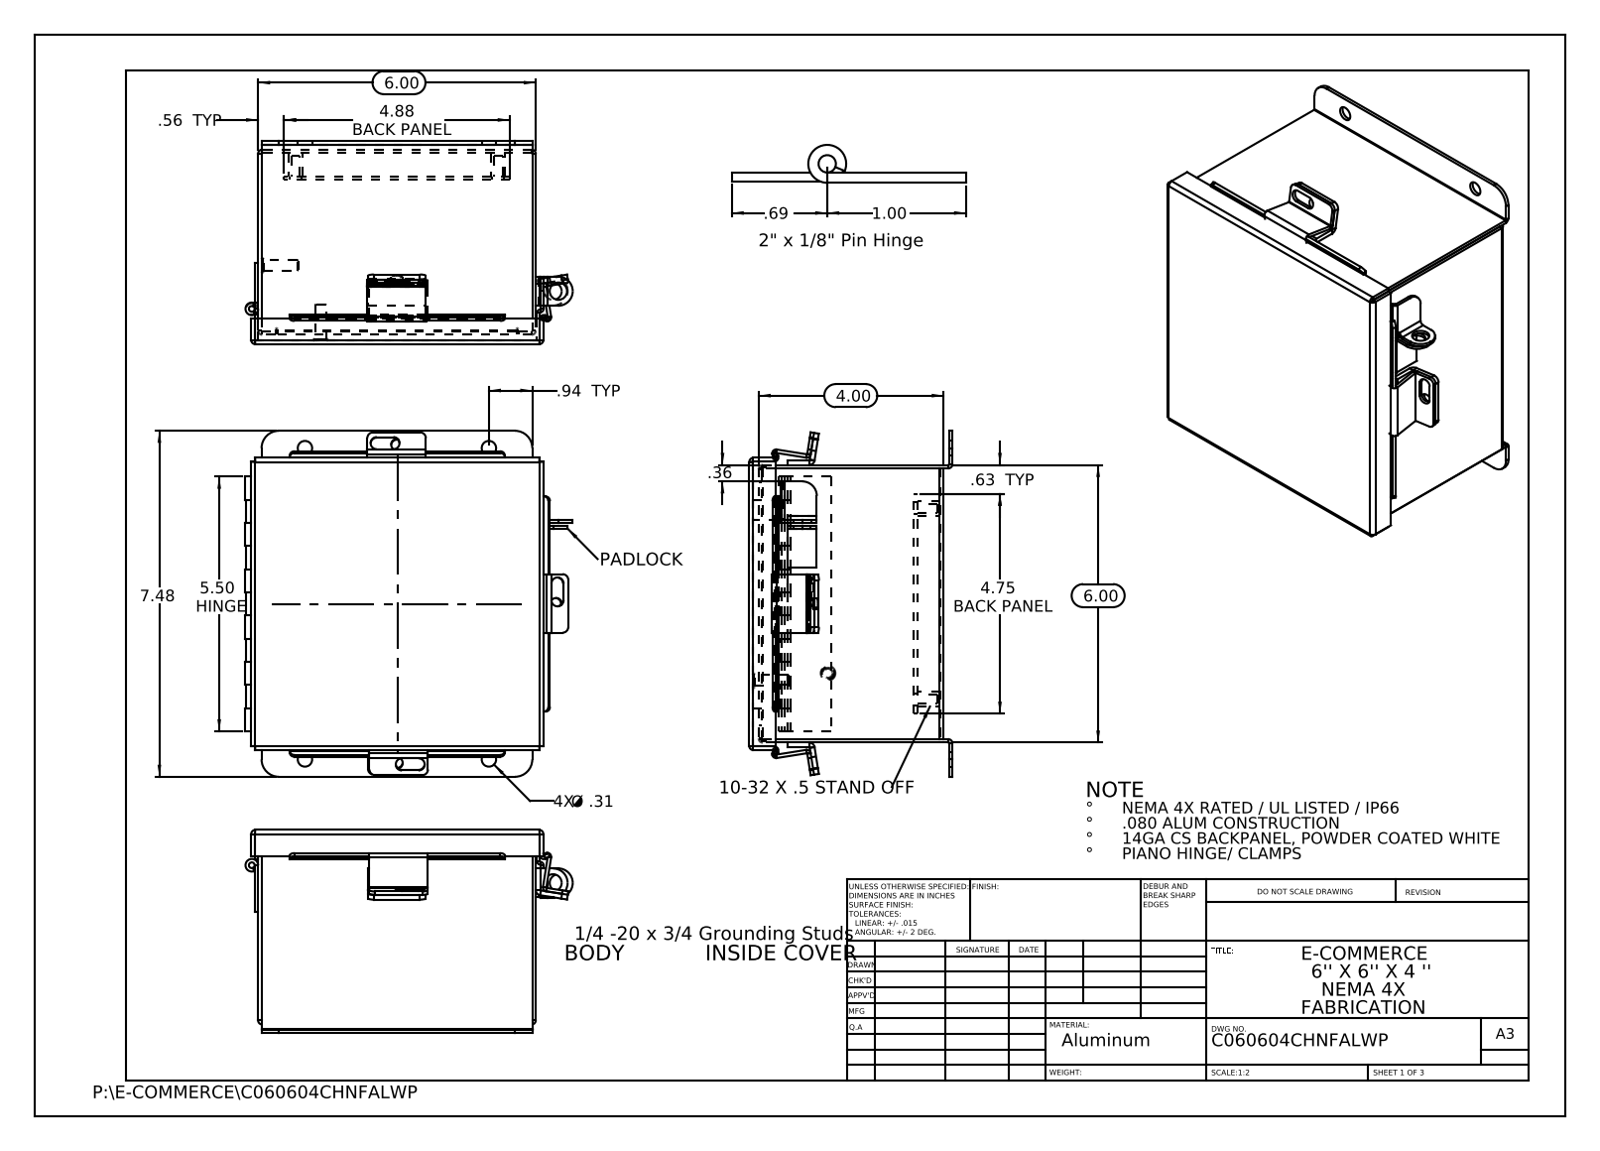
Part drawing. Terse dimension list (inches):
name: C060604CHNFALWP JIC Backpanel; C060604CHNFALWP Hinge Cover Side JIC; C060604CHNFALWP JIC Enclosure Template; HW-CLH-JH-20154 (+8 more)
written by: SolidWorks 2013 (CONFIG_CONTROL_DESIGN)
unit: in
bodies: 21 solids, 548 faces (343 planar, 185 cylindrical, 20 other)
size: 7.476 × 7.072 × 4.39
volume: 18.33 in³; area: 507.2 in²
holes: 7× ⌀0.25, 4× ⌀0.187, 4× ⌀0.312, 1× ⌀0.125, 1× ⌀0.125, 1× ⌀0.373, 1× ⌀0.375
bosses: 4× ⌀0.313, 2× ⌀0.315, 2× ⌀0.236, 1× ⌀0.273, 1× ⌀0.25
rounds: 13× R0.013, 12× R0.009, 12× R0.088, 10× R0.125, 6× R0.083, 6× R0.1, 6× R0.133, 4× R0.375
face distances: 0.075, 5.925, 4.128, 5.85, 6, 4.053, 4.203, 0.074, 0.575, 0.5
hole spacings: 1.315, 4.373, 5.43, 6.846, 3.976, 4.126, 4.375, 6.013
